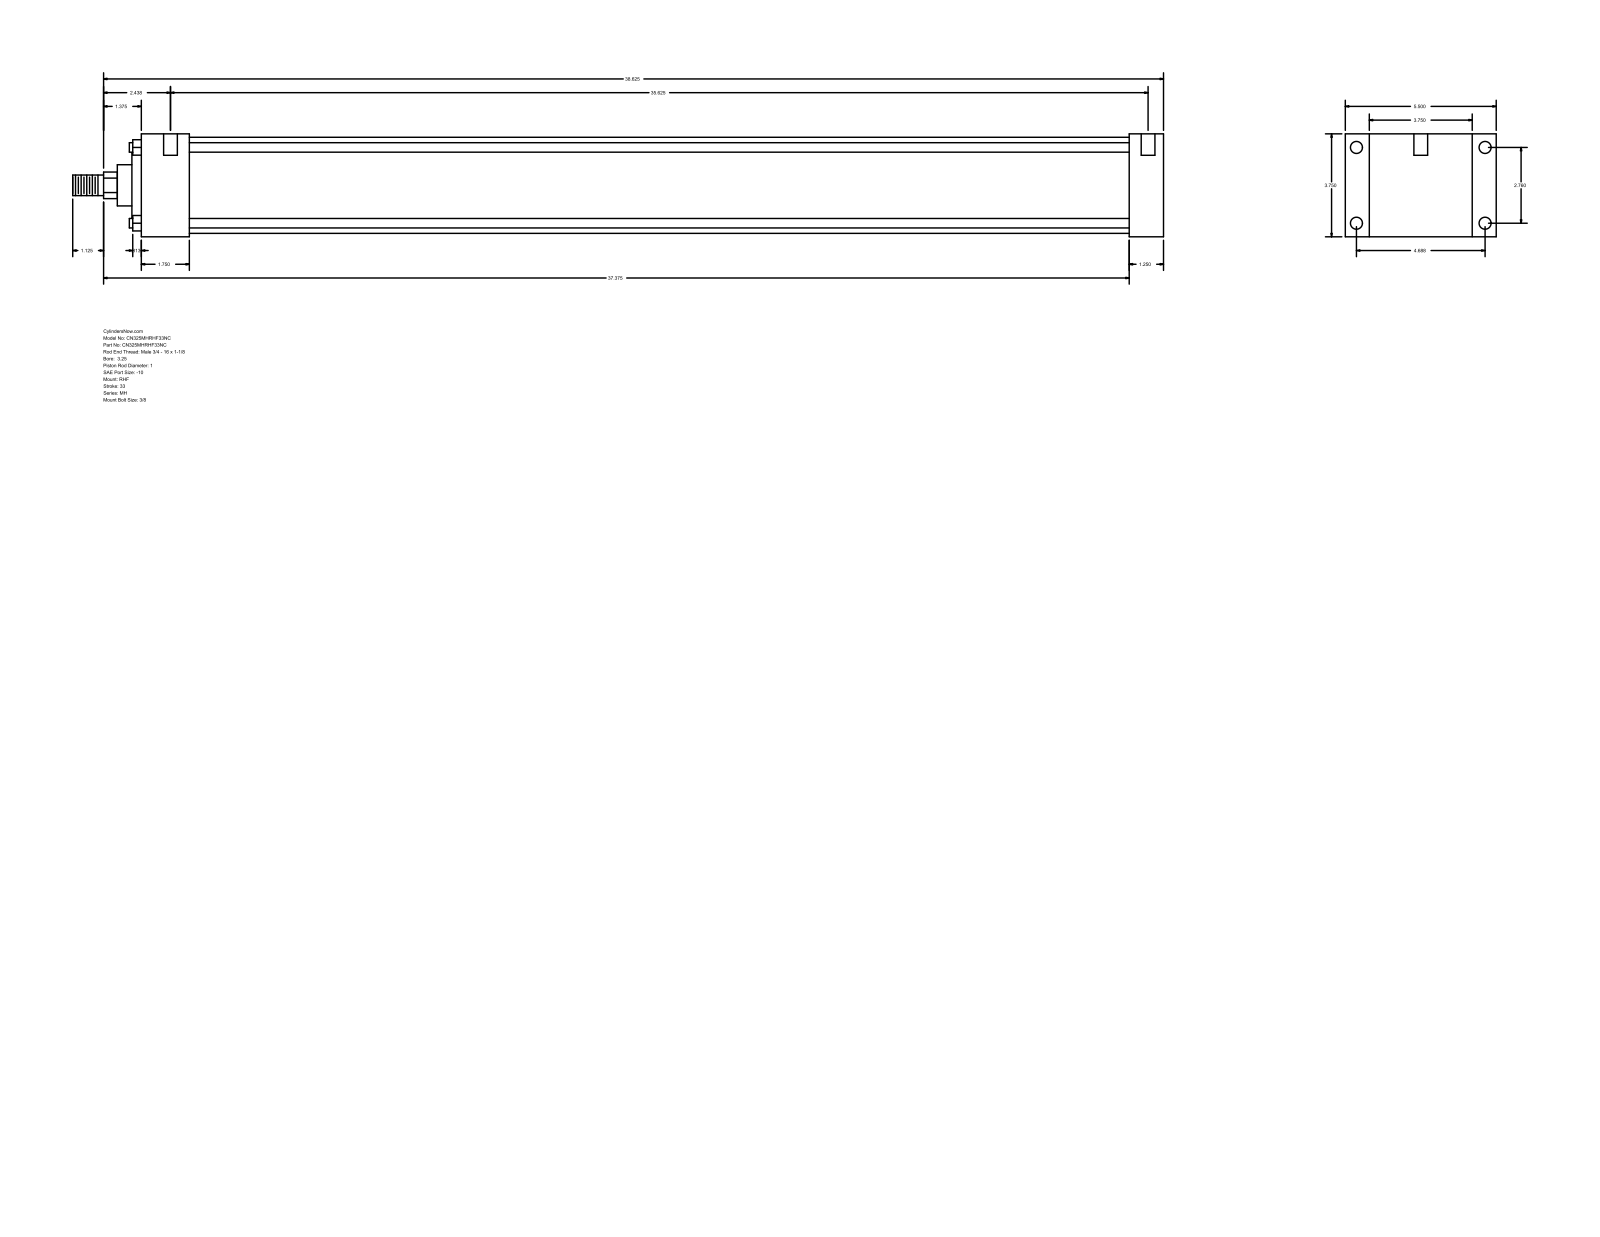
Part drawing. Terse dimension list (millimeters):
name: MH_RHF__0325_1
written by: GSSL Pune (CONFIG_CONTROL_DESIGN)
unit: mm
bodies: 0 solids, 90 faces (61 planar, 29 cylindrical, 0 other)
size: 1009.65 × 139.7 × 95.25
holes: 4× ⌀5.56, 4× ⌀11.13, 2× ⌀12.7
bosses: 4× ⌀8.76, 1× ⌀88.9, 1× ⌀60.33, 1× ⌀38.1, 1× ⌀25.4, 1× ⌀19.05
rounds: 1× R12.29
face distances: 95.24, 31.75, 22.23, 117.47, 914.41, 946.16, 139.7, 44.46, 869.95, 901.7
hole spacings: 70.1, 119.06, 138.16, 911.22, 1.58, 4.76, 904.88, 906.46
